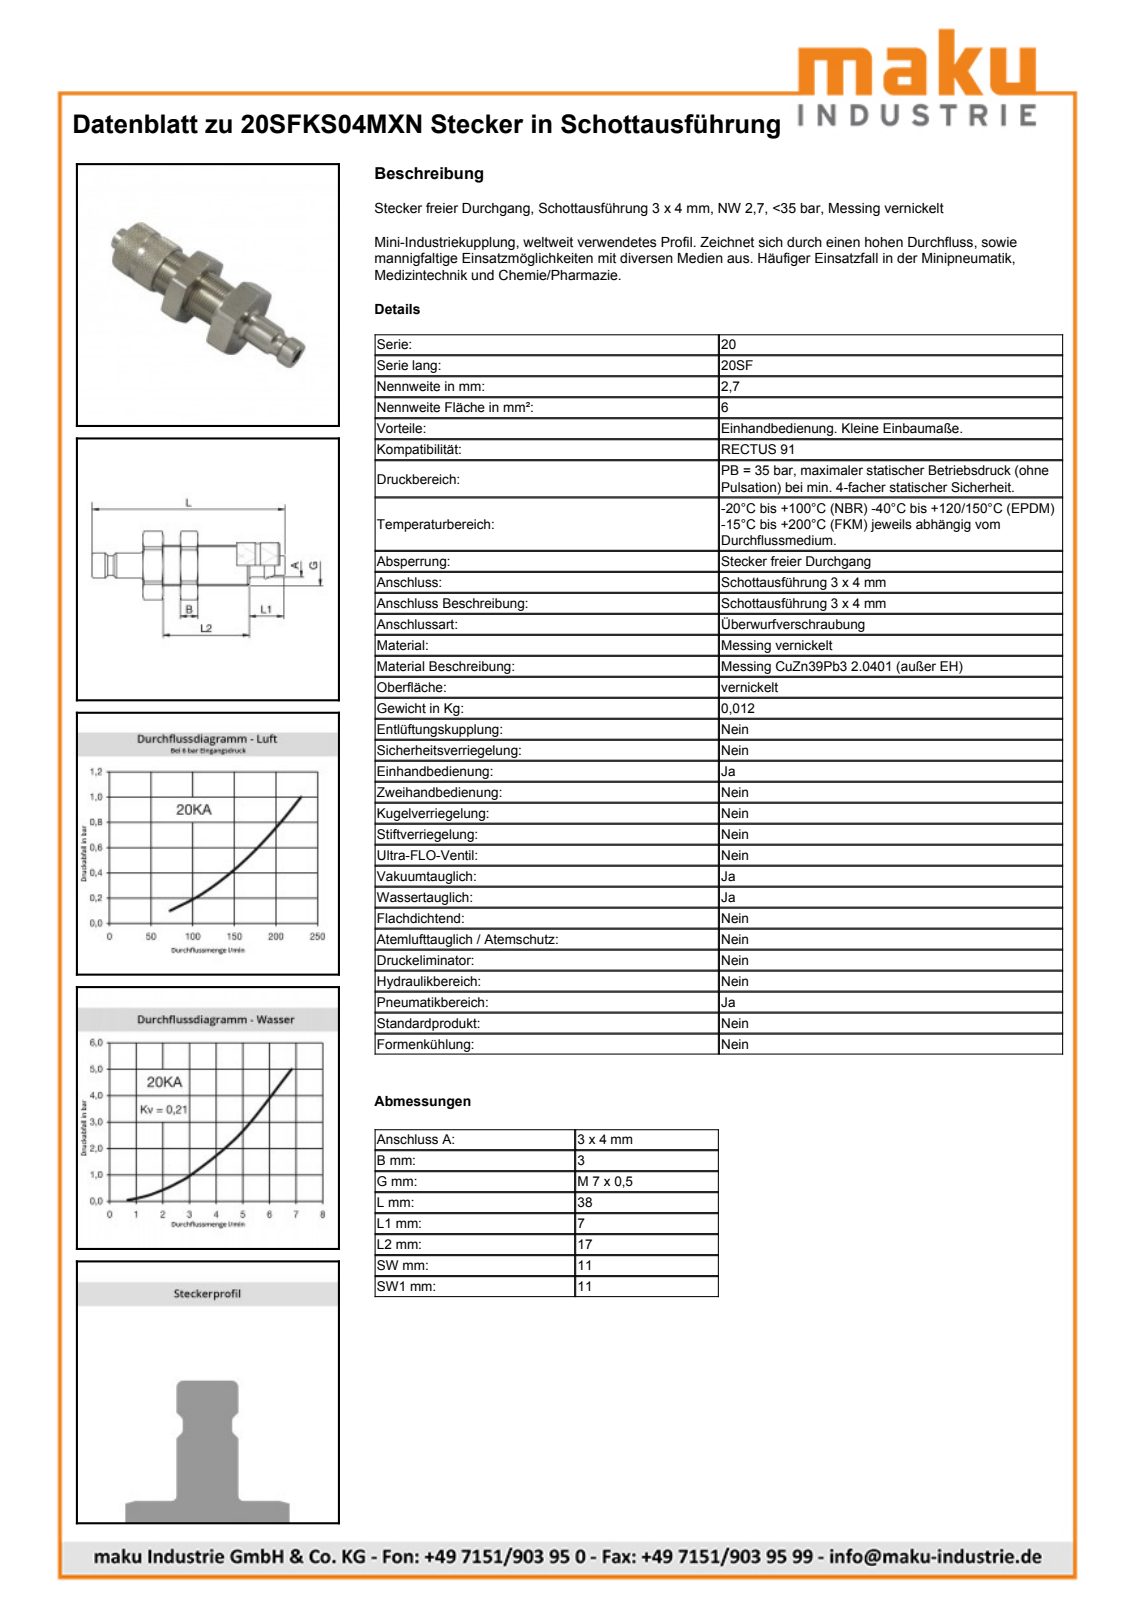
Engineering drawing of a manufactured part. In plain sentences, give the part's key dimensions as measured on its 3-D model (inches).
The part is named "D111896; D111892; D104103; D111898". Its 3-D file was written by "Autodesk Inventor 2013 (AUTOMOTIVE_DESIGN)". It is 3 solids with 92 faces: 24 planar, 27 cylindrical and 41 other. Overall it measures 1.502 by 0.488 by 0.433 inches. Its volume is 0.093 cubic inches and its surface area 3.072 square inches. Round holes: 1 of diameter 0.077, 1 of diameter 0.106, 1 of diameter 0.167, 1 of diameter 0.254, 1 of diameter 0.256. Round bosses or shafts: 1 of diameter 0.319, 1 of diameter 0.303, 1 of diameter 0.276, 1 of diameter 0.244, 1 of diameter 0.197, 1 of diameter 0.156, 1 of diameter 0.138, 1 of diameter 0.112. Partial cylindrical surfaces (rounded edges, fillets, slot ends): 1 of radius 0.244. The main face-to-face distances are 0.433, 0.118, 0.208, 0.326, 0.157, 0.169, 0.051, 0.782, 0.9, 0.951.
